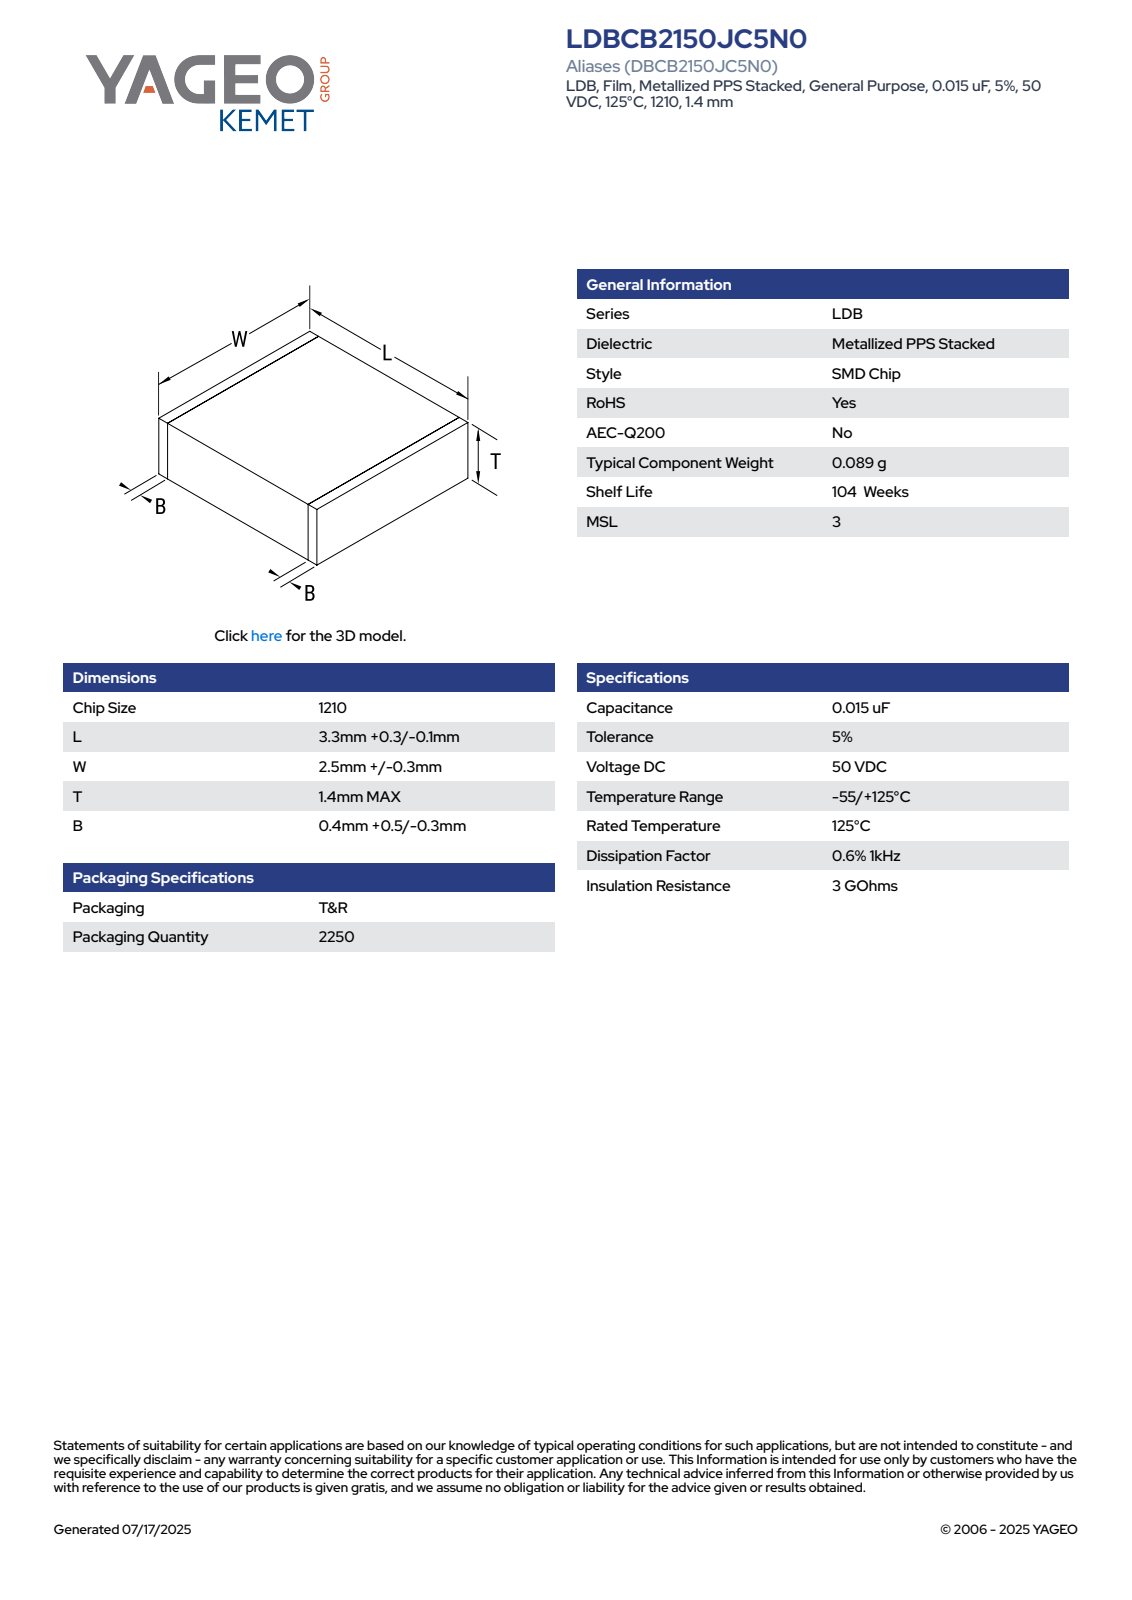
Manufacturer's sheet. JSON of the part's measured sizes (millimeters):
{"part_name": "CFS_LDELDB_1210_L3.6W2.8T1.4B0.9", "step_written_by": "SolidWorks 2020 (AUTOMOTIVE_DESIGN)", "units": "millimeters", "bodies": {"solids": 4, "faces": 73, "planar": 73, "cylindrical": 0, "other": 0}, "overall_size": [3.6, 2.8, 1.4], "volume_mm3": 14, "surface_area_mm2": 39, "face_to_face_distances": [1.38, 1.39, 3.6, 2.78, 1.4, 2.79, 2.8, 0.5, 3.1, 2.6]}
